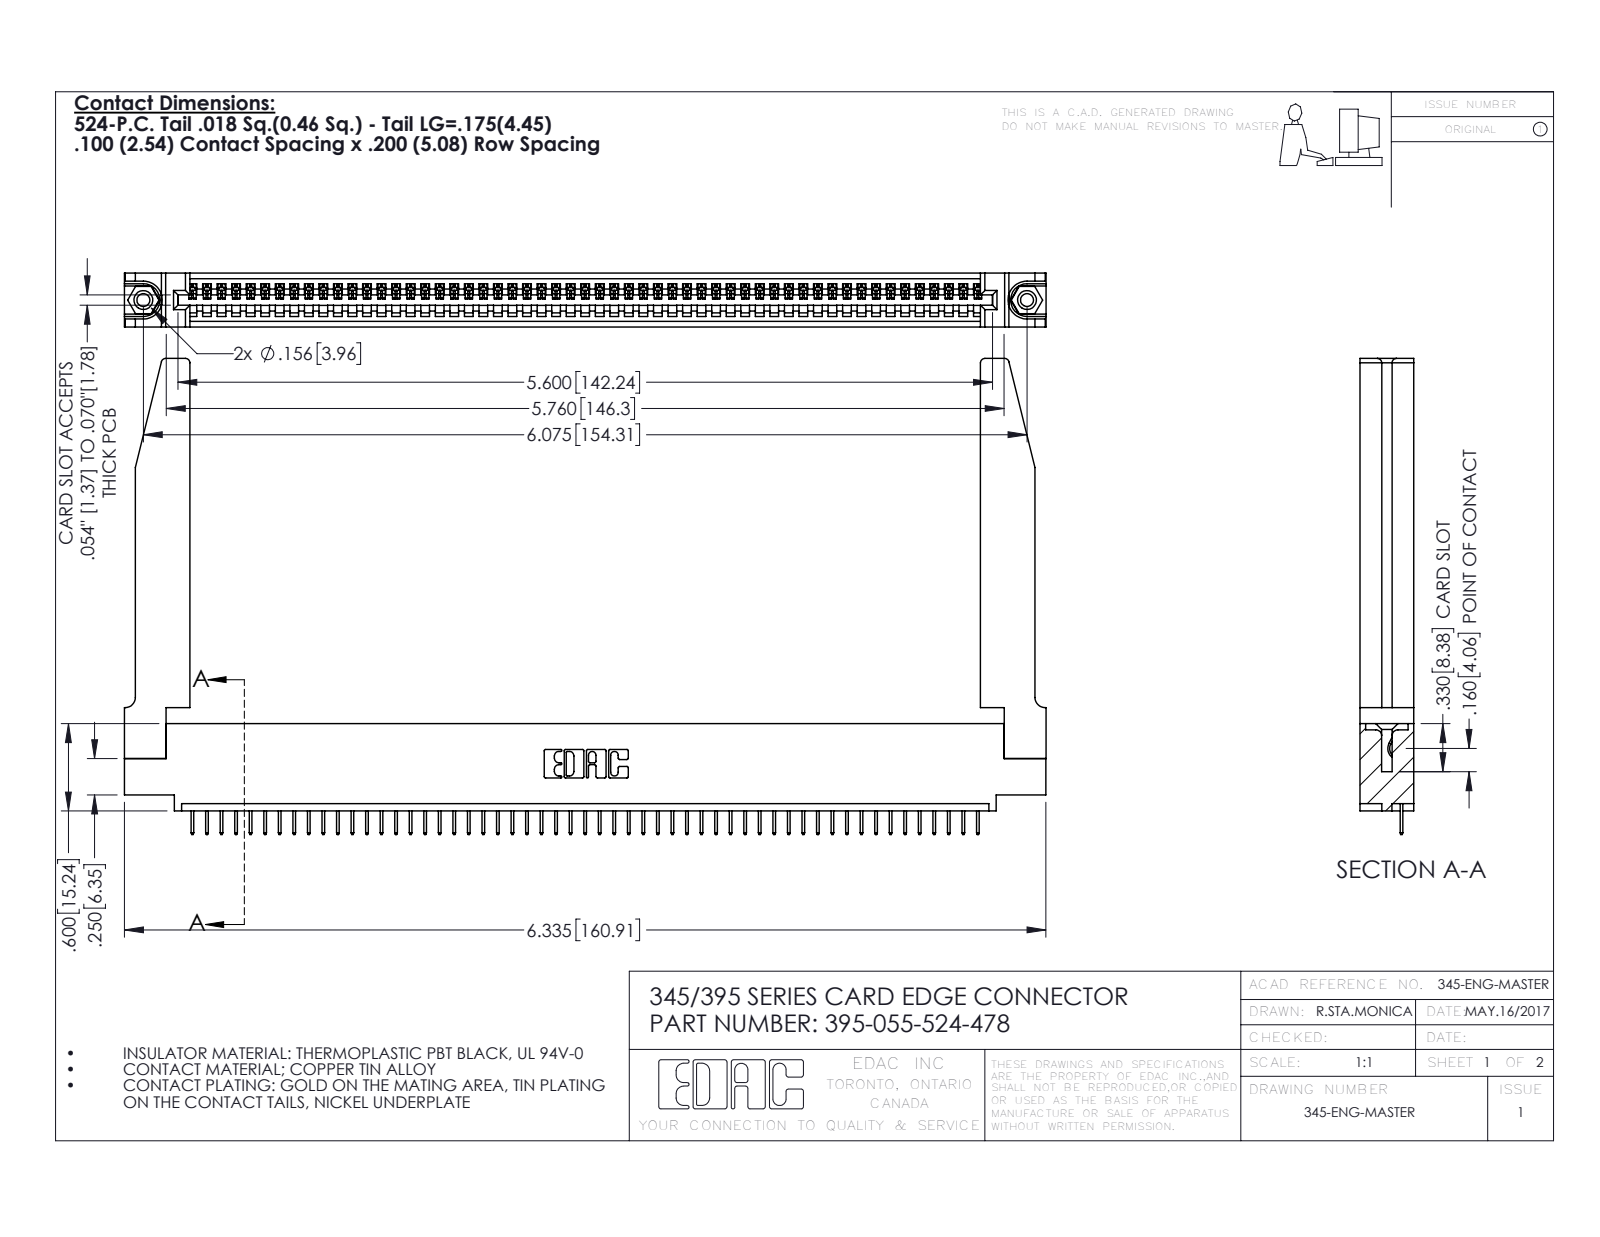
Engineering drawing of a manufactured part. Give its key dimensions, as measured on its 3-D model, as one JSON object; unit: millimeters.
{"part_name": "345 Part_0.110 Offset - 0.156 Dia-TH; 345-292-001_345-293-124; 395-055-524-478; 345-250-001_345-250-001-102 (+1 more)", "step_written_by": "SolidWorks 2016 (CONFIG_CONTROL_DESIGN)", "units": "millimeters", "bodies": {"solids": 60, "faces": 3774, "planar": 2756, "cylindrical": 966, "other": 52}, "overall_size": [160.9, 83.1, 9.4], "volume_mm3": 22880, "surface_area_mm2": 26480, "round_holes": [[2.3, 2], [3.2, 2], [4, 2], [1.6, 1]], "round_bosses_or_shafts": [[3.9, 2]], "partial_cylinders_radius": [[0.2, 110], [0.3, 22], [0.8, 8], [0.2, 6], [0.8, 6], [0.7, 3], [0.8, 2], [1, 2]], "face_to_face_distances": [9.4, 1.8, 7.6, 5.1, 2.5, 6.9, 0.6, 5.7, 1.8, 3.8], "hole_center_spacings": [6.9, 148.3, 154.3]}
